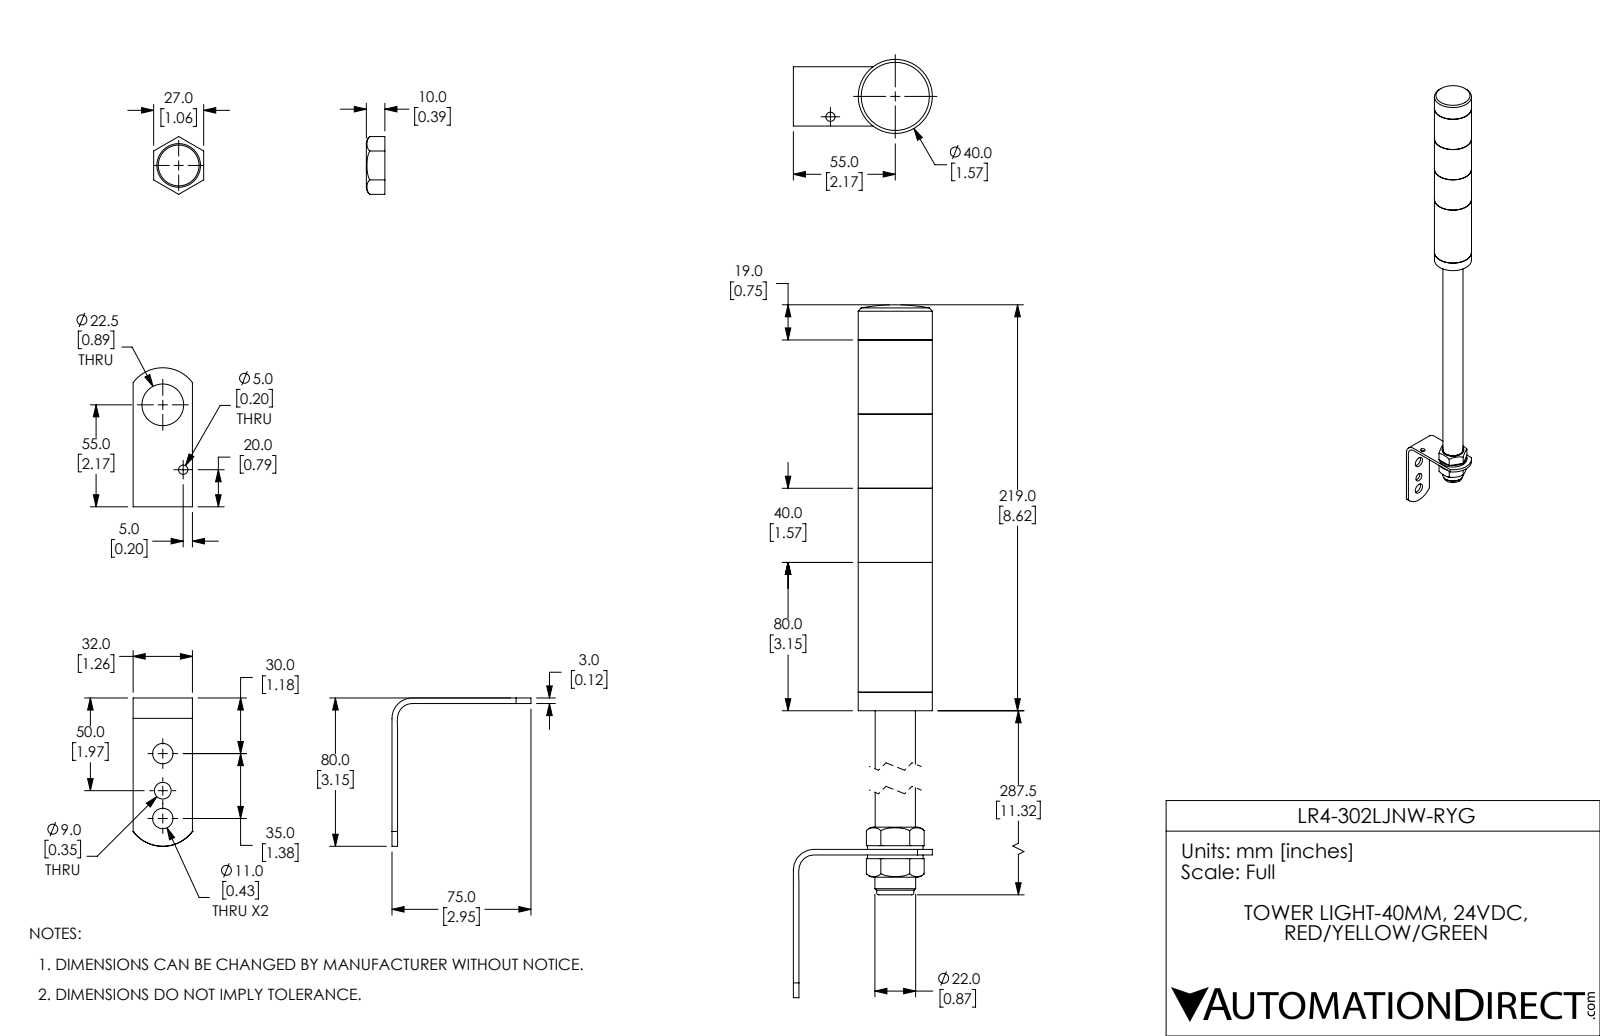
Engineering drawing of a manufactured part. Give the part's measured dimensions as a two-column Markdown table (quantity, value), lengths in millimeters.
| quantity | value |
| --- | --- |
| part name | LR4-302LJNW-RYG |
| STEP written by | SolidWorks 2017 (AUTOMOTIVE_DESIGN) |
| units | millimeters |
| bodies | 12 solids, 162 faces (58 planar, 89 cylindrical, 15 other) |
| overall size | 562 × 75 × 40 |
| volume | 340 000 mm³ |
| surface area | 112 100 mm² |
| round holes (diameter × count) | 3.2 × 2, 11 × 2, 5 × 1, 7.7 × 1, 9 × 1, 17.7 × 1, 22 × 1, 22.5 × 1, 27.6 × 1, 34.7 × 1, 35.2 × 1, 35.3 × 1 |
| round bosses / shafts (diameter × count) | 40 × 1, 30 × 1, 21.7 × 1 |
| partial cylindrical surfaces (radius × count) | 20 × 1 |
| main face-to-face distances | 40, 80, 120, 90.3, 10.3, 66, 106, 146, 186, 130.3 |
| hole center spacings | 7.2, 14.4, 15, 20, 29.9, 35, 36.7, 43.6 |
